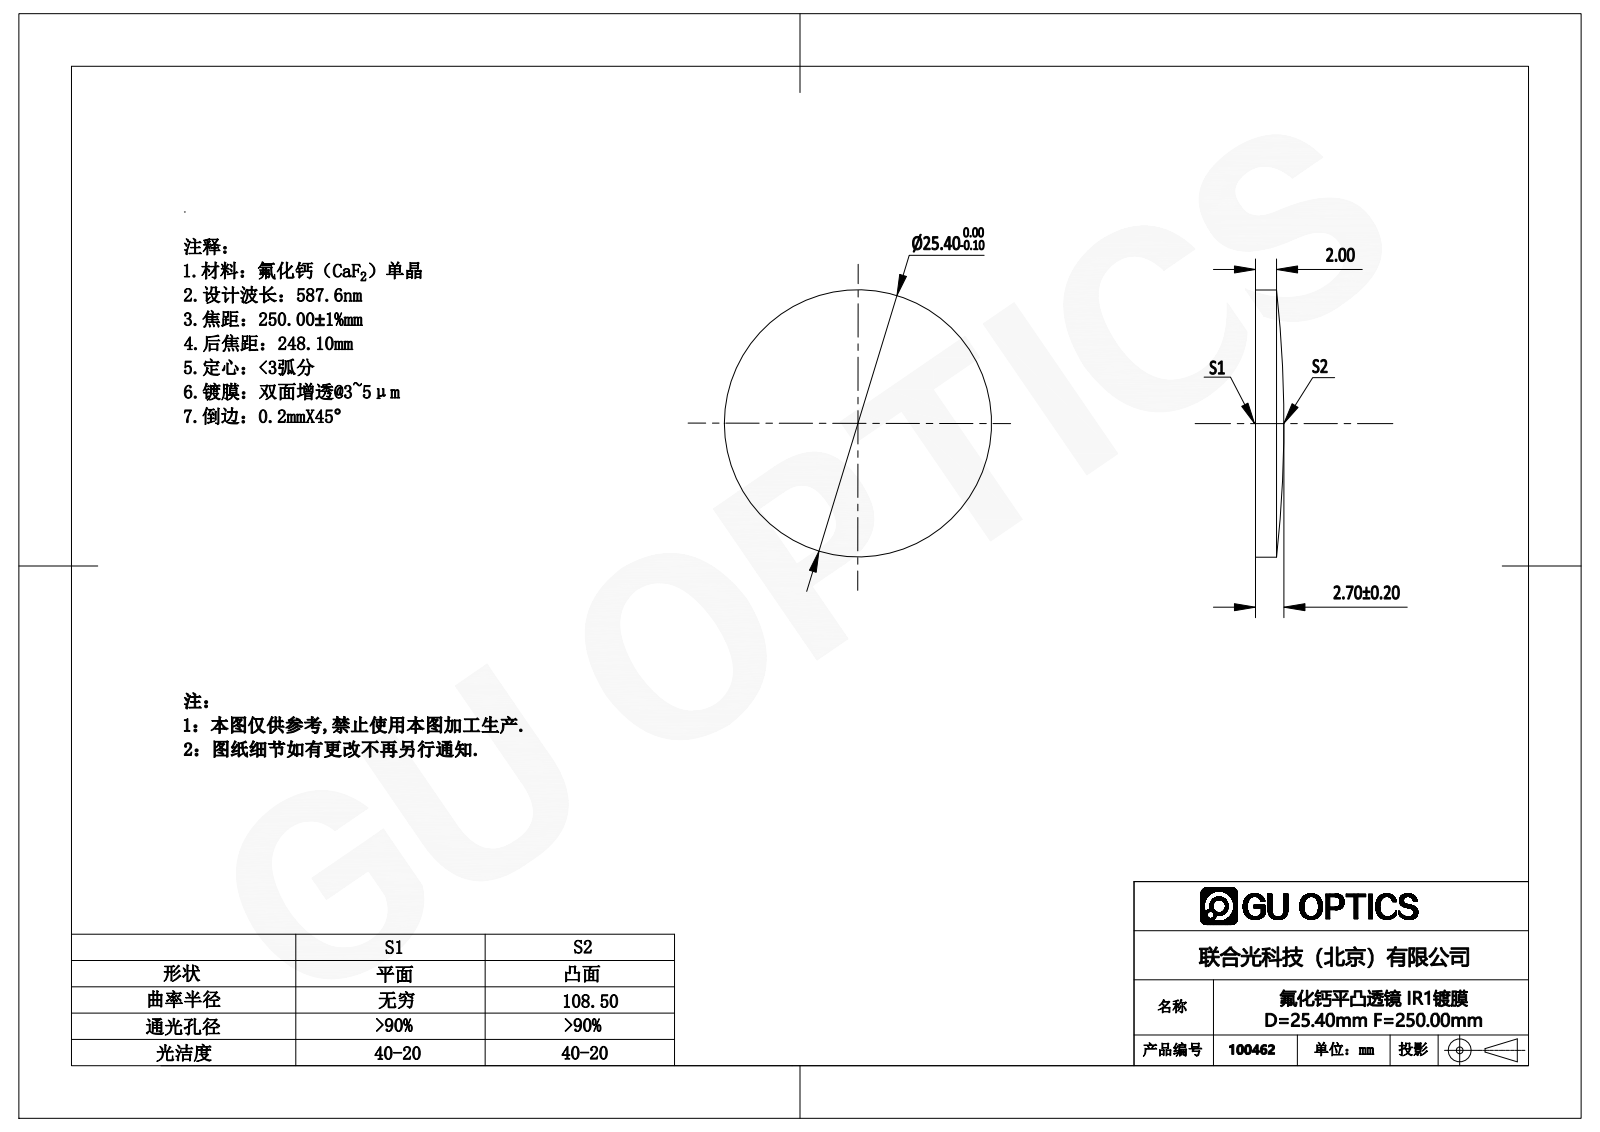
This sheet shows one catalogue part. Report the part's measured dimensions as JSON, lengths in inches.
{"part_name": "100452", "step_written_by": "SolidWorks 2016 (AUTOMOTIVE_DESIGN)", "units": "inches", "bodies": {"solids": 1, "faces": 5, "planar": 1, "cylindrical": 2, "other": 2}, "overall_size": [1, 1, 0.106], "volume_in3": 0.073, "surface_area_in2": 1.821, "round_bosses_or_shafts": [[1, 1]]}
